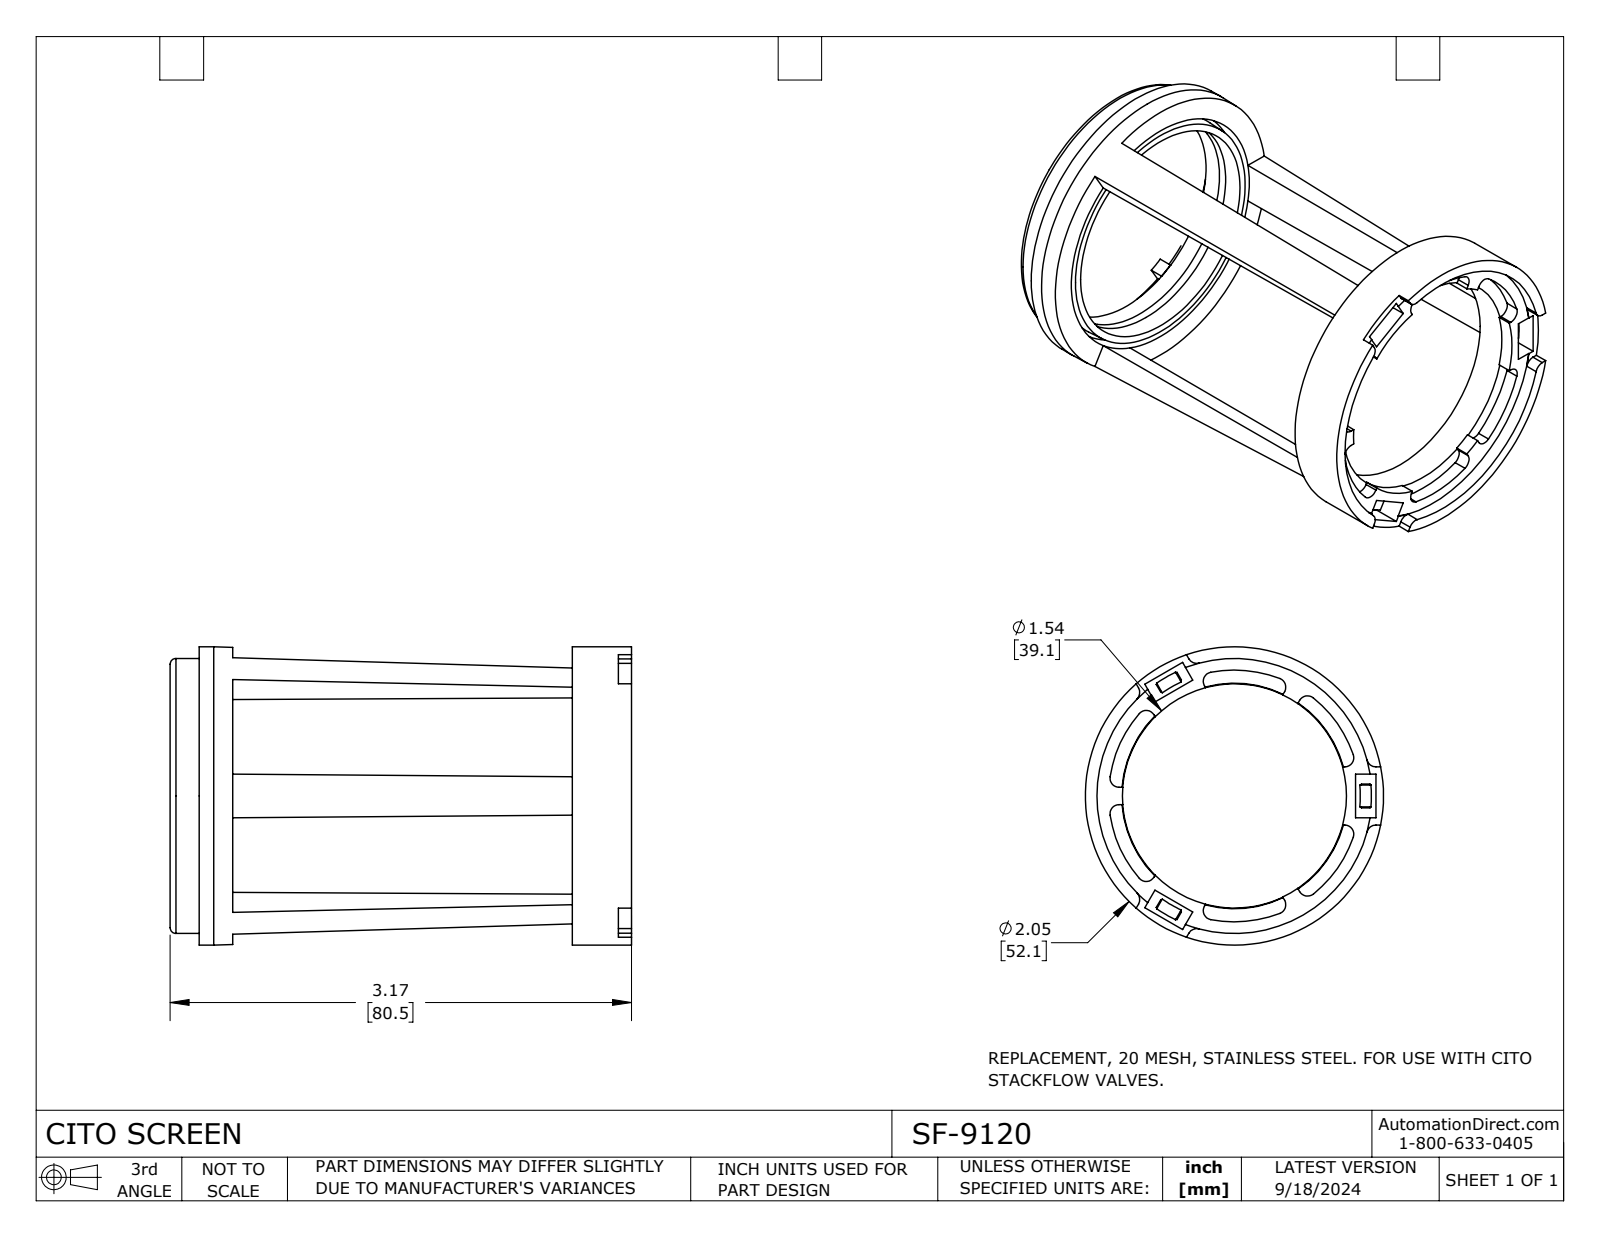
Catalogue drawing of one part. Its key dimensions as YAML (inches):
part_name: "SF-9120"
step_written_by: "SolidWorks 2023 (CONFIG_CONTROL_DESIGN)"
units: inches
bodies: {solids: 2, faces: 191, planar: 112, cylindrical: 65, other: 14}
overall_size: [3.171, 2.05, 2.05]
volume: 1.085
surface_area: 23.95
round_holes:
  - {diameter: 1.55, count: 1}
  - {diameter: 1.73, count: 1}
  - {diameter: 1.89, count: 1}
round_bosses_or_shafts:
  - {diameter: 2.05, count: 1}
  - {diameter: 1.65, count: 1}
partial_cylinders:
  - {radius: 0.062, count: 10}
  - {radius: 0.063, count: 8}
  - {radius: 0.77, count: 1}
  - {radius: 0.771, count: 1}
face_to_face_distances: [2.335, 0.1, 2.649, 0.314, 0.23, 2.565, 2.879, 2.979, 0.33, 2.665]
